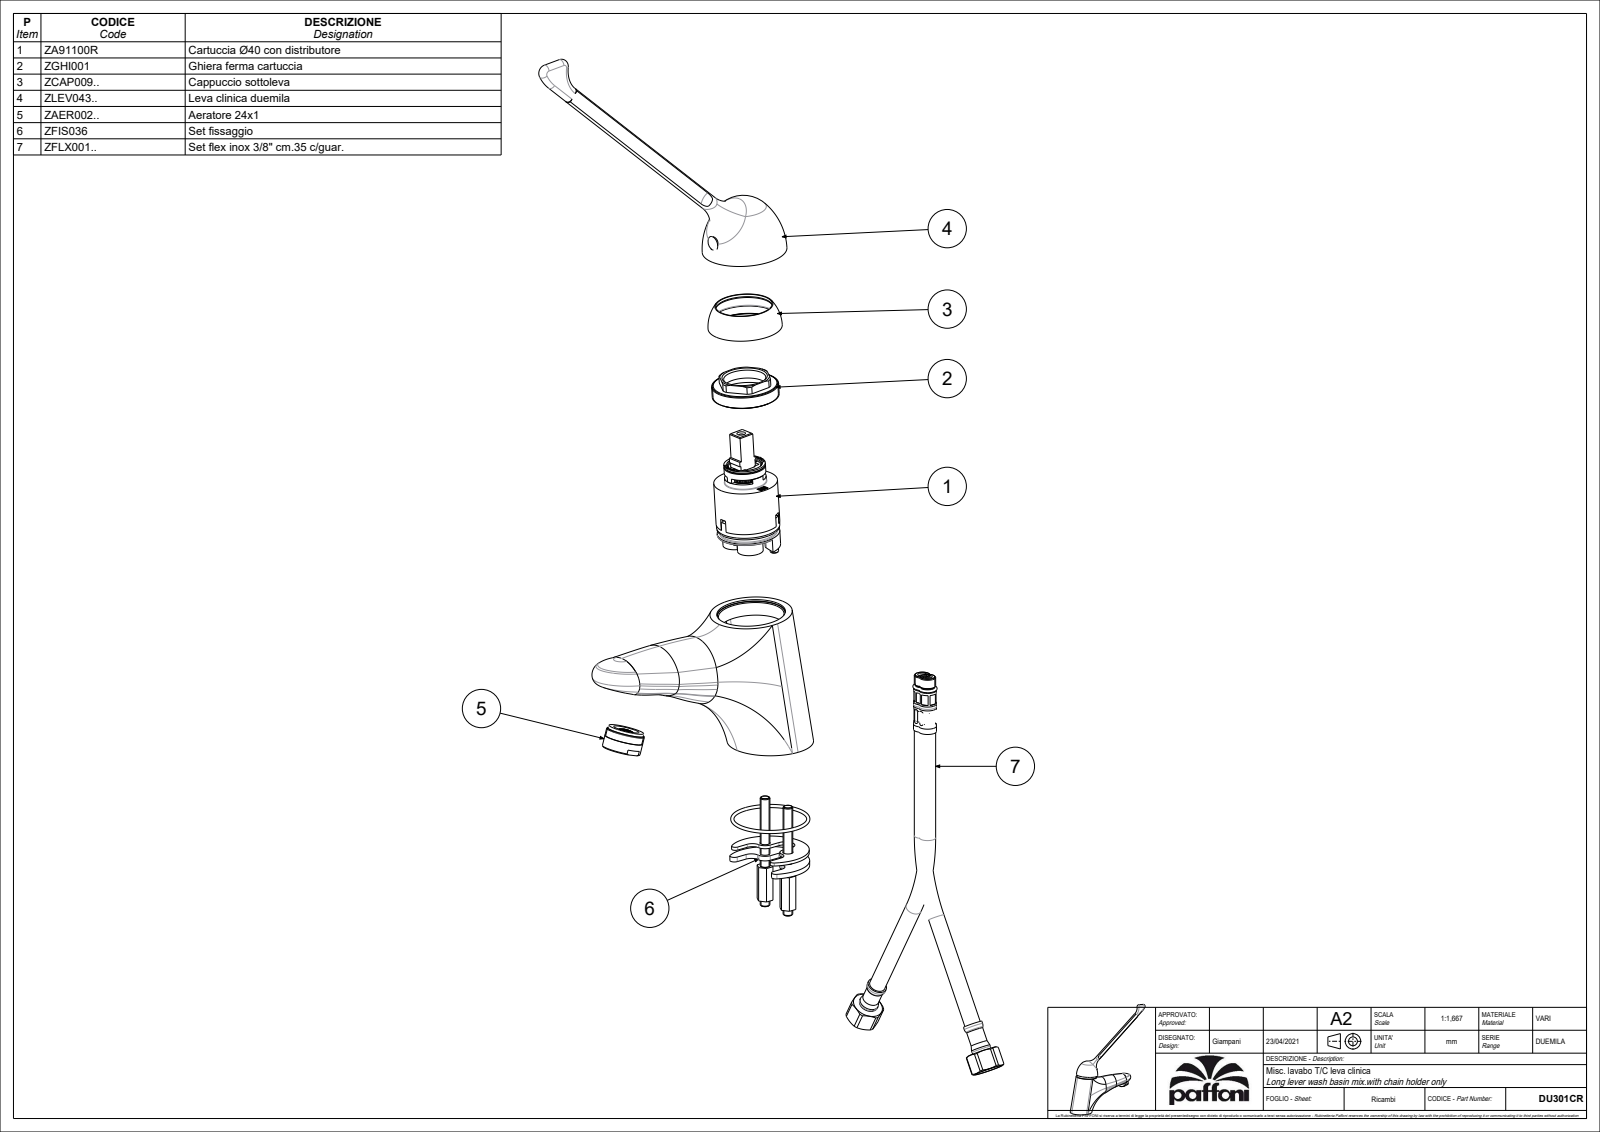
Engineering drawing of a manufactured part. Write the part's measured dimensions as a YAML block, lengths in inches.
part_name: "DU301CR"
step_written_by: "CREO PARAMETRIC BY PTC INC, 2020044 (CONFIG_CONTROL_DESIGN)"
units: inches
bodies: {solids: 1, faces: 237, planar: 50, cylindrical: 62, other: 125}
overall_size: [9.997, 8.125, 2.106]
volume: 18.06
surface_area: 97.92
round_holes:
  - {diameter: 0.207, count: 2}
  - {diameter: 0.217, count: 2}
  - {diameter: 0.276, count: 2}
  - {diameter: 0.315, count: 2}
  - {diameter: 0.354, count: 2}
  - {diameter: 0.433, count: 2}
  - {diameter: 0.197, count: 1}
  - {diameter: 0.236, count: 1}
  - {diameter: 0.965, count: 1}
  - {diameter: 1.539, count: 1}
  - {diameter: 1.594, count: 1}
  - {diameter: 1.598, count: 1}
round_bosses_or_shafts:
  - {diameter: 1.752, count: 1}
  - {diameter: 0.945, count: 1}
  - {diameter: 0.394, count: 1}
  - {diameter: 0.315, count: 1}
partial_cylinders:
  - {radius: 0.118, count: 2}
  - {radius: 0.157, count: 1}
  - {radius: 0.62, count: 1}
face_to_face_distances: [0.236, 2.028, 2.402, 0.374, 0.189, 0.425, 0.315, 0.079, 0.11, 0.504]
hole_center_spacings: [0.339, 0.615, 0.432, 0.476, 0.53, 0.591, 0.622, 0.89]
